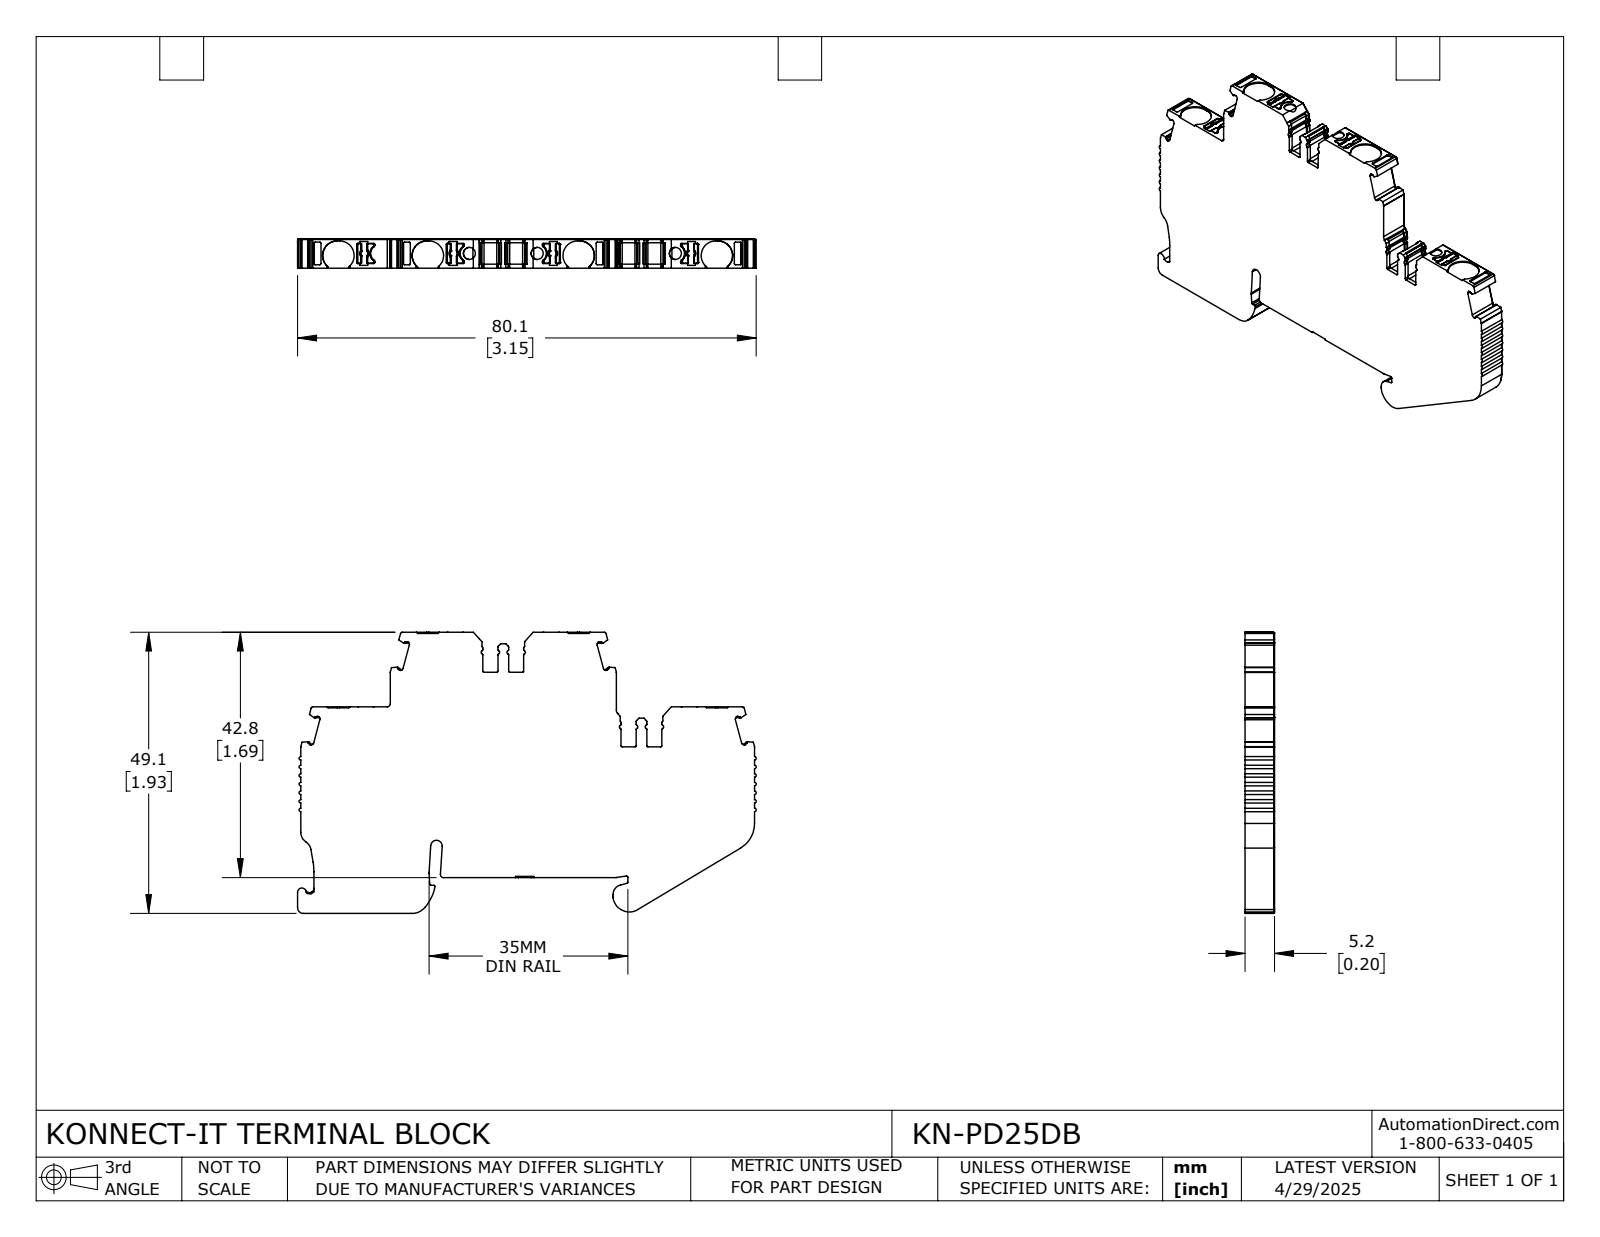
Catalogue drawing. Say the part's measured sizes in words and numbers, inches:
The part is named "KN-PD25DB". Its 3-D file was written by "SolidWorks 2024 (CONFIG_CONTROL_DESIGN)". It is 1 solid with 979 faces: 470 planar, 438 cylindrical and 71 other. Overall it measures 3.153 by 1.933 by 0.203 inches. Its volume is 0.889 cubic inches and its surface area 11.63 square inches. Round holes: 3 of diameter 0.083. Partial cylindrical surfaces (rounded edges, fillets, slot ends): 100 of radius 0.008, 57 of radius 0.012, 41 of radius 0.004, 21 of radius 0.02, 17 of radius 0.016, 16 of radius 0.006, 9 of radius 0.024, 8 of radius 0.006. The main face-to-face distances are 0.203, 0.512, 0.246, 1.678, 1.166, 1.924, 0.079, 1.412, 0.504, 0.95. The hole center spacings are 0.466, 0.95, 1.417.
